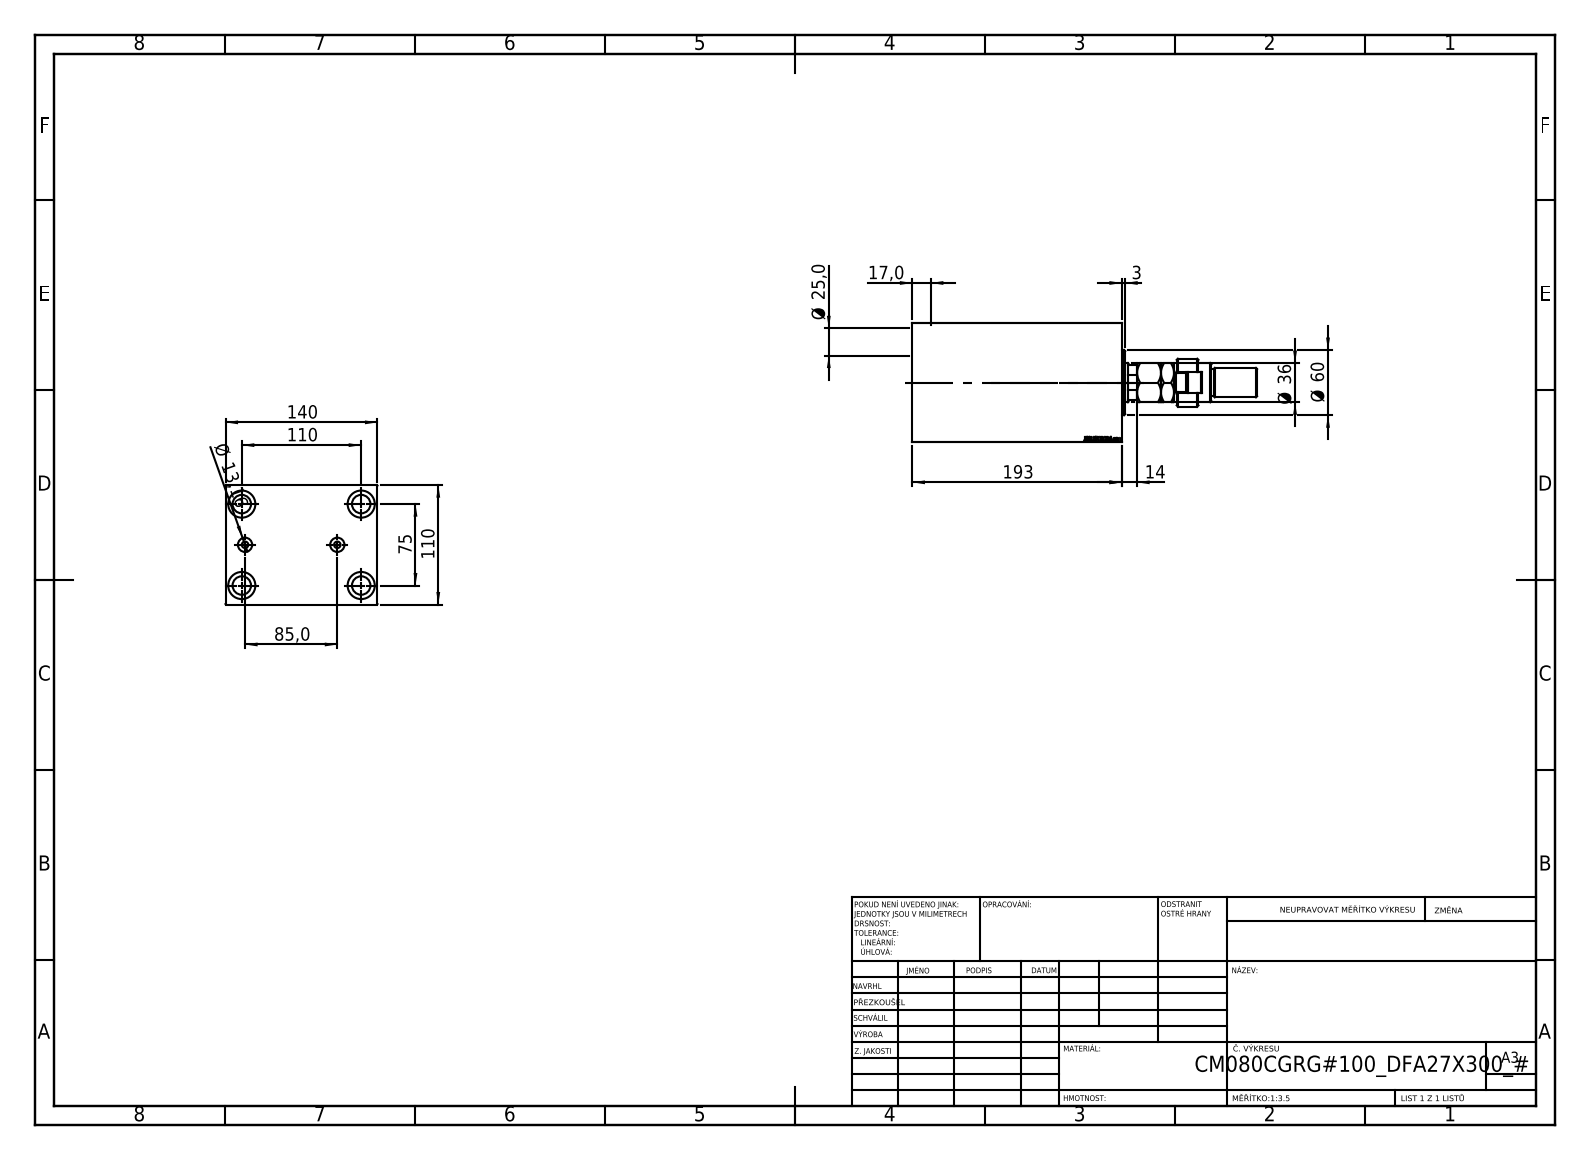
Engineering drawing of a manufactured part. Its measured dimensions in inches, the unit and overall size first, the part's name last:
Units: inches
Overall size (bounding box): 12.5 × 5.512 × 4.331
Round holes (diameter × count): ⌀0.669 ×4, ⌀0.984 ×4, ⌀0.236 ×2, ⌀0.518 ×2, ⌀1.004 ×1, ⌀1.555 ×1, ⌀3.15 ×1, ⌀3.228 ×1, ⌀3.425 ×1
Round bosses / shafts (diameter × count): ⌀2.362 ×1, ⌀1.732 ×1, ⌀1.417 ×1, ⌀1.102 ×1, ⌀1.063 ×1, ⌀0.984 ×1, ⌀0.709 ×1
Partial cylindrical surfaces — rounded edges, fillets, slot ends (radius × count): R0.374 ×1, R0.591 ×1, R0.689 ×1
Main face-to-face distances: 4.331, 5.512, 7.598, 6.772, 0.827, 0.551, 7.047, 6.22, 3.937, 4.488
Hole centre spacings: 2.621, 1.481, 1.712, 2.953, 3.766, 4.331, 4.464, 5.242
Volume: 149.6 in³ · Surface area: 459.3 in²
Bodies: 5 solids, 945 faces (436 planar, 71 cylindrical, 438 other)
Part name (STEP PRODUCT): V450CM_C_VCP; MFA; FEMALE_PART_FOR_DFA; V450CM_VC_B (+1 more)
STEP written by: SolidWorks 2019 (CONFIG_CONTROL_DESIGN)
